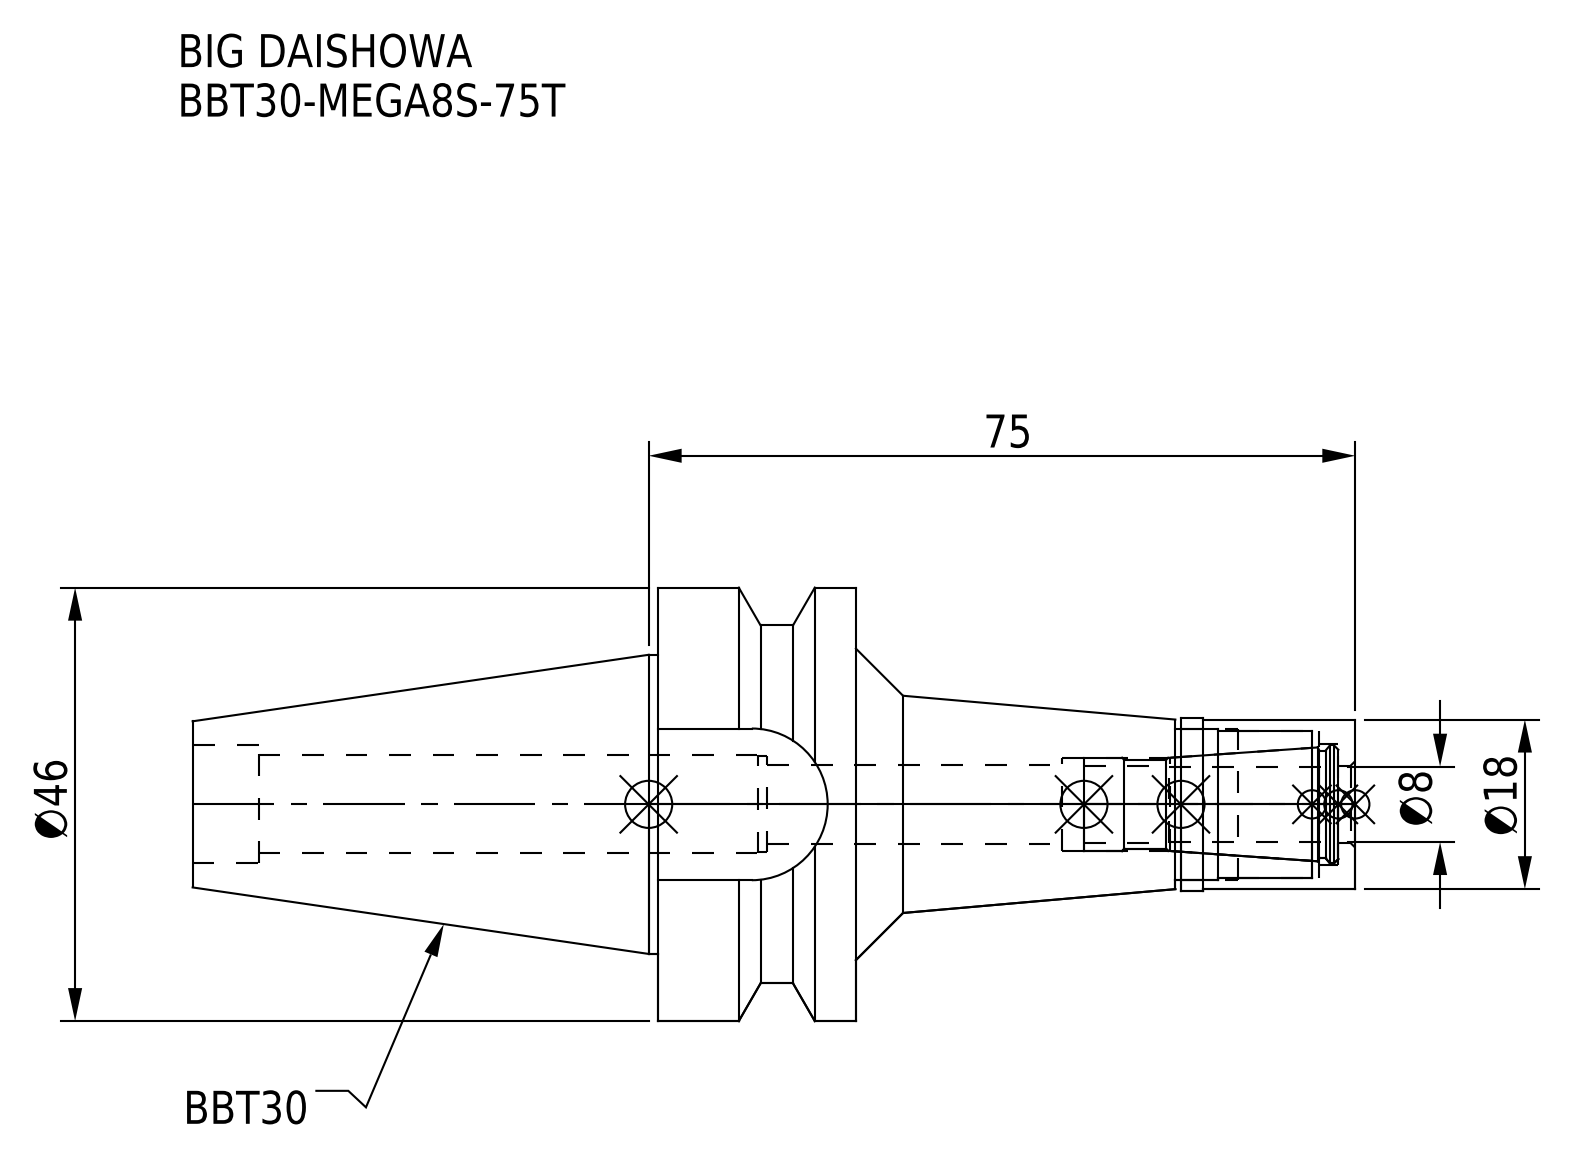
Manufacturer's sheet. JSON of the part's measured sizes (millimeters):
{"part_name": "BBT30-MEGA8S-75T.stp; DXF_TEMP_ASSY_ASM_4_ASM.stp; MGN8S_1.stp; BBT30-MEGA8S-75T (+3 more)", "step_written_by": "SolidWorks 2019 (CONFIG_CONTROL_DESIGN)", "units": "millimeters", "bodies": {"solids": 2, "faces": 74, "planar": 22, "cylindrical": 38, "other": 14}, "overall_size": [123.4, 46, 46], "volume_mm3": 61398, "surface_area_mm2": 18749, "round_holes": [[8.2, 1], [8.4, 1], [9.9, 1], [10.2, 1], [10.4, 1], [12.5, 1], [12.9, 1], [15.6, 1], [16.1, 1]], "round_bosses_or_shafts": [[46, 1], [31.75, 1], [18.3, 1], [18, 1]], "partial_cylinders_radius": [[8.05, 1], [19, 1]], "face_to_face_distances": [21, 32.6, 53, 74, 123.4, 70.4, 49.4, 16.1, 4.6, 48.4]}
